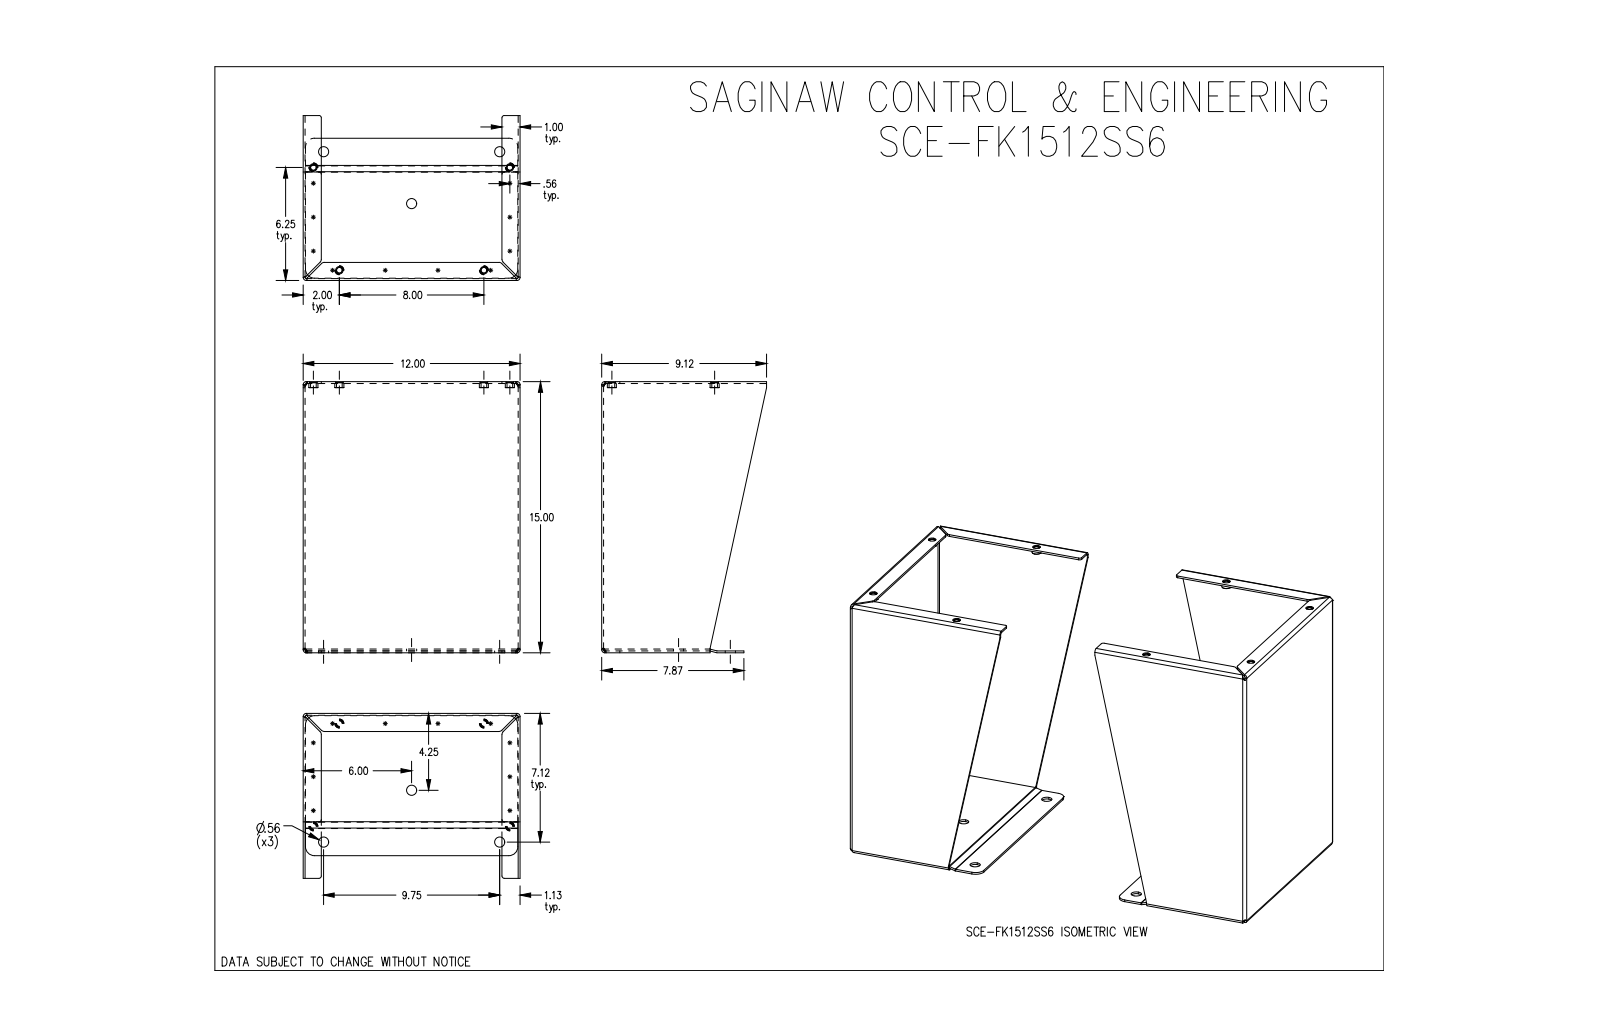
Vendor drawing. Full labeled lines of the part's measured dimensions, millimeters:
Part name (STEP PRODUCT): SCE-FK1512SS6
STEP written by: SolidWorks 2019 (CONFIG_CONTROL_DESIGN)
Units: millimetres
Bodies: 12 solids, 286 faces (120 planar, 110 cylindrical, 56 other)
Overall size (bounding box): 609.6 × 381 × 304.8
Volume: 1 822 000 mm³ · Surface area: 1 400 000 mm²
Round holes (diameter × count): ⌀7.9 ×8, ⌀10.5 ×8, ⌀14.3 ×6
Round bosses / shafts (diameter × count): ⌀12.7 ×8, ⌀10.5 ×8
Partial cylindrical surfaces — rounded edges, fillets, slot ends (radius × count): R4.2 ×16, R1.6 ×12, R3.2 ×8, R5.6 ×8, R12.7 ×8, R1.6 ×4
Main face-to-face distances: 2.6, 302.2, 607, 304.8, 299.5, 604.3, 609.6, 375.7, 378.4, 2.6
Hole centre spacings: 26.3, 138.2, 143.7, 147.1, 149, 168, 270.4, 279.9
